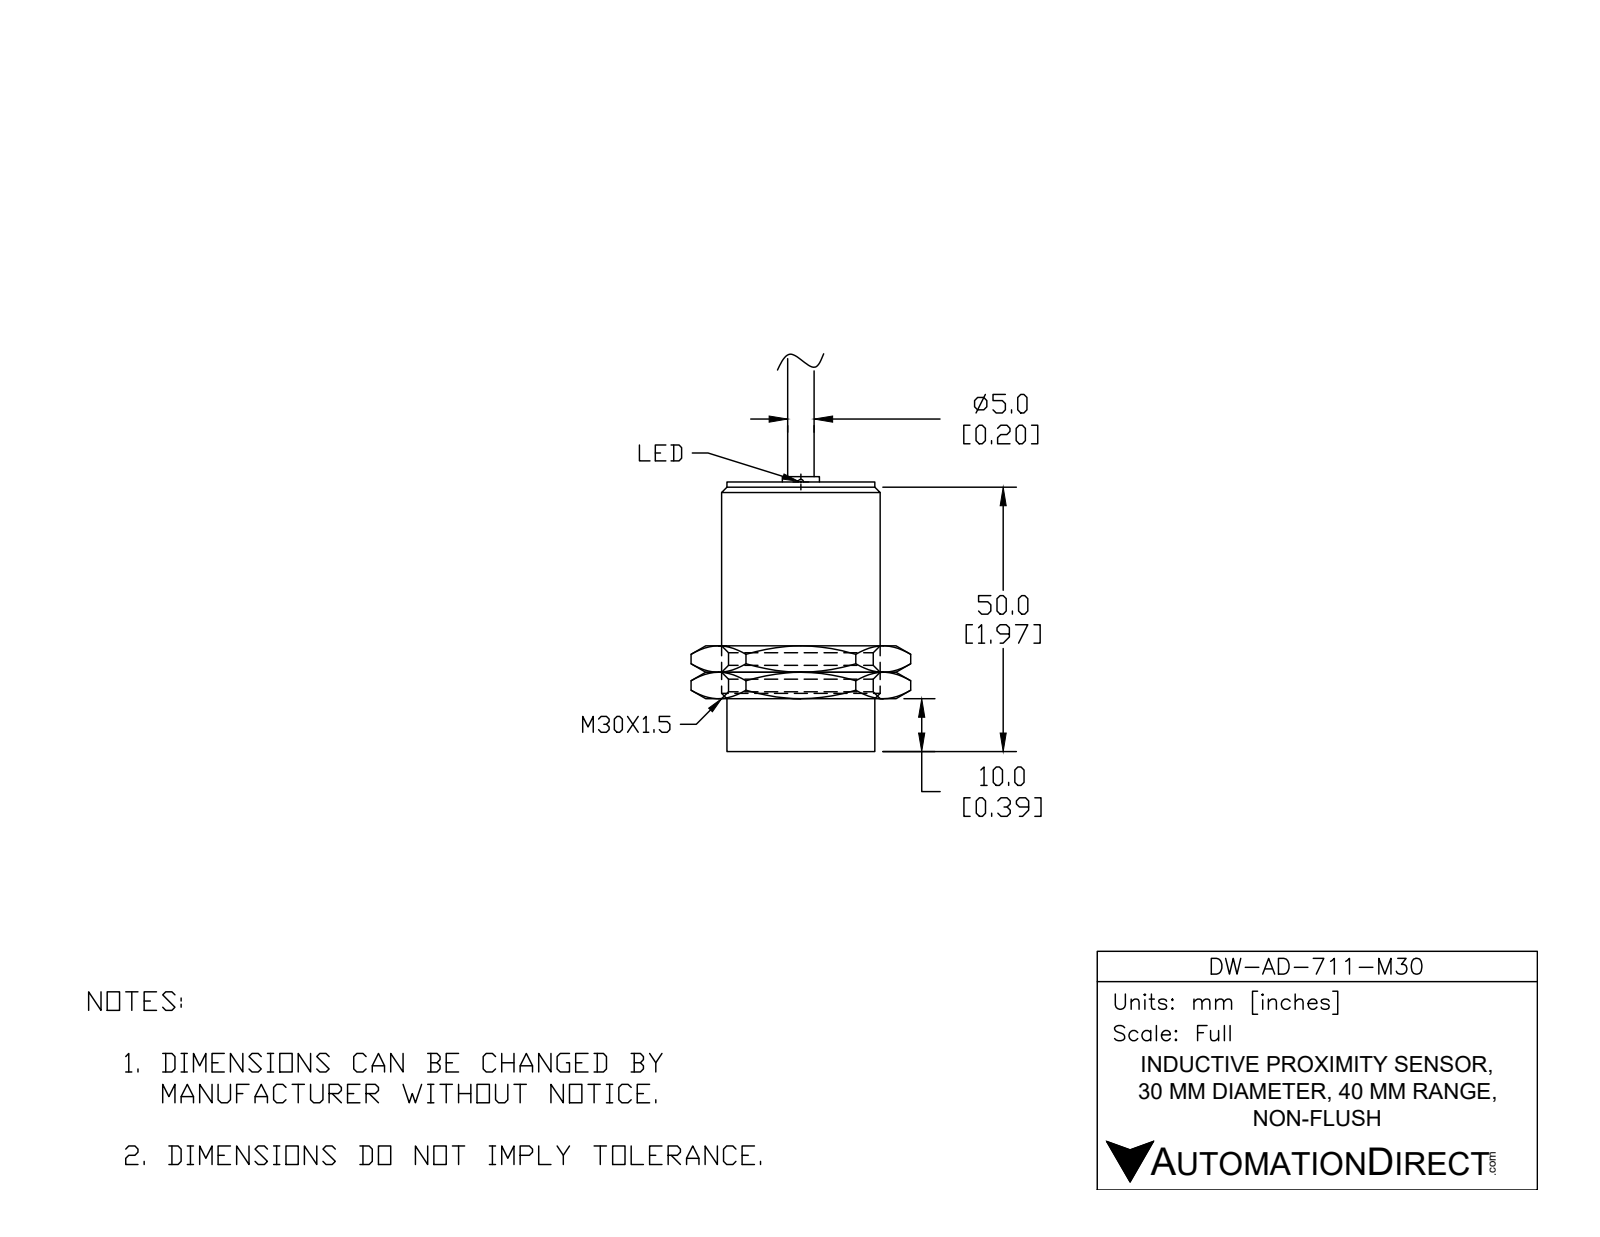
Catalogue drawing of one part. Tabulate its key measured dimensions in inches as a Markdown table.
| quantity | value |
| --- | --- |
| part name | DW-AD-711-M30 |
| STEP written by | SolidWorks 2017 (AUTOMOTIVE_DESIGN) |
| units | inches |
| bodies | 2 solids, 37 faces (18 planar, 7 cylindrical, 12 other) |
| overall size | 3.016 × 1.181 × 1.181 |
| volume | 2.159 in³ |
| surface area | 10.1 in² |
| round bosses / shafts (diameter × count) | 1.181 × 1, 1.083 × 1, 0.413 × 1, 0.268 × 1, 0.197 × 1, 0.118 × 1 |
| main face-to-face distances | 2.008, 0.031, 2.087, 0.079, 2.039, 0.047, 1.89, 0.118, 0.15, 0.197 |
